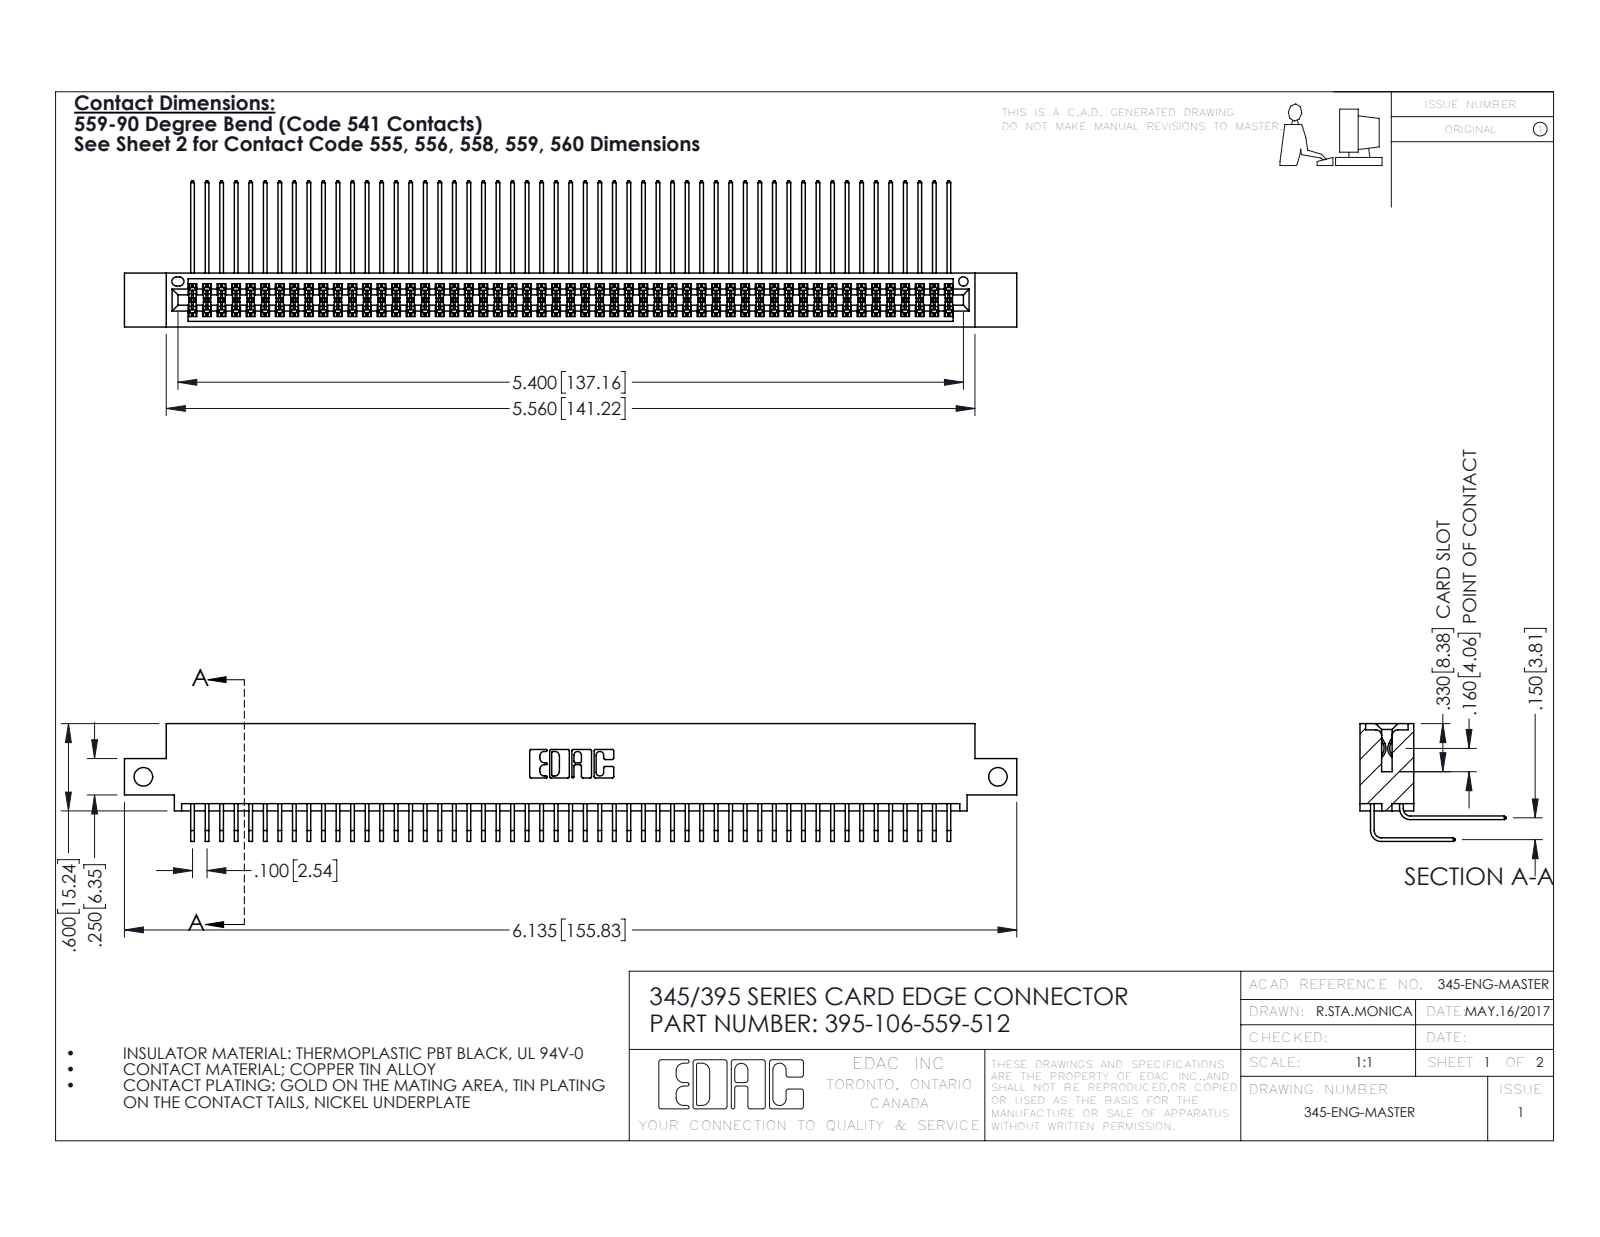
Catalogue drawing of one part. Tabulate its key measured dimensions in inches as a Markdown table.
| quantity | value |
| --- | --- |
| part name | 345-292-001_558 559 Tail - 1; 395-106-559-512; 345-292-001_559 Tail - 2; 345 Part_0.110 Offset - Side Mount |
| STEP written by | SolidWorks 2016 (CONFIG_CONTROL_DESIGN) |
| units | inches |
| bodies | 107 solids, 5642 faces (3794 planar, 1848 cylindrical, 0 other) |
| overall size | 6.135 × 1.005 × 0.809 |
| volume | 0.957 in³ |
| surface area | 40.67 in² |
| round holes (diameter × count) | 0.128 × 2, 0.064 × 1 |
| partial cylindrical surfaces (radius × count) | 0.006 × 159, 0.01 × 22, 0.007 × 6, 0.031 × 6, 0.026 × 3, 0.014 × 2, 0.019 × 2, 0.022 × 2 |
| main face-to-face distances | 0.072, 0.298, 0.2, 0.37, 0.098, 0.272, 0.025, 0.225, 0.175, 0.15 |
| hole center spacings | 5.875 |
